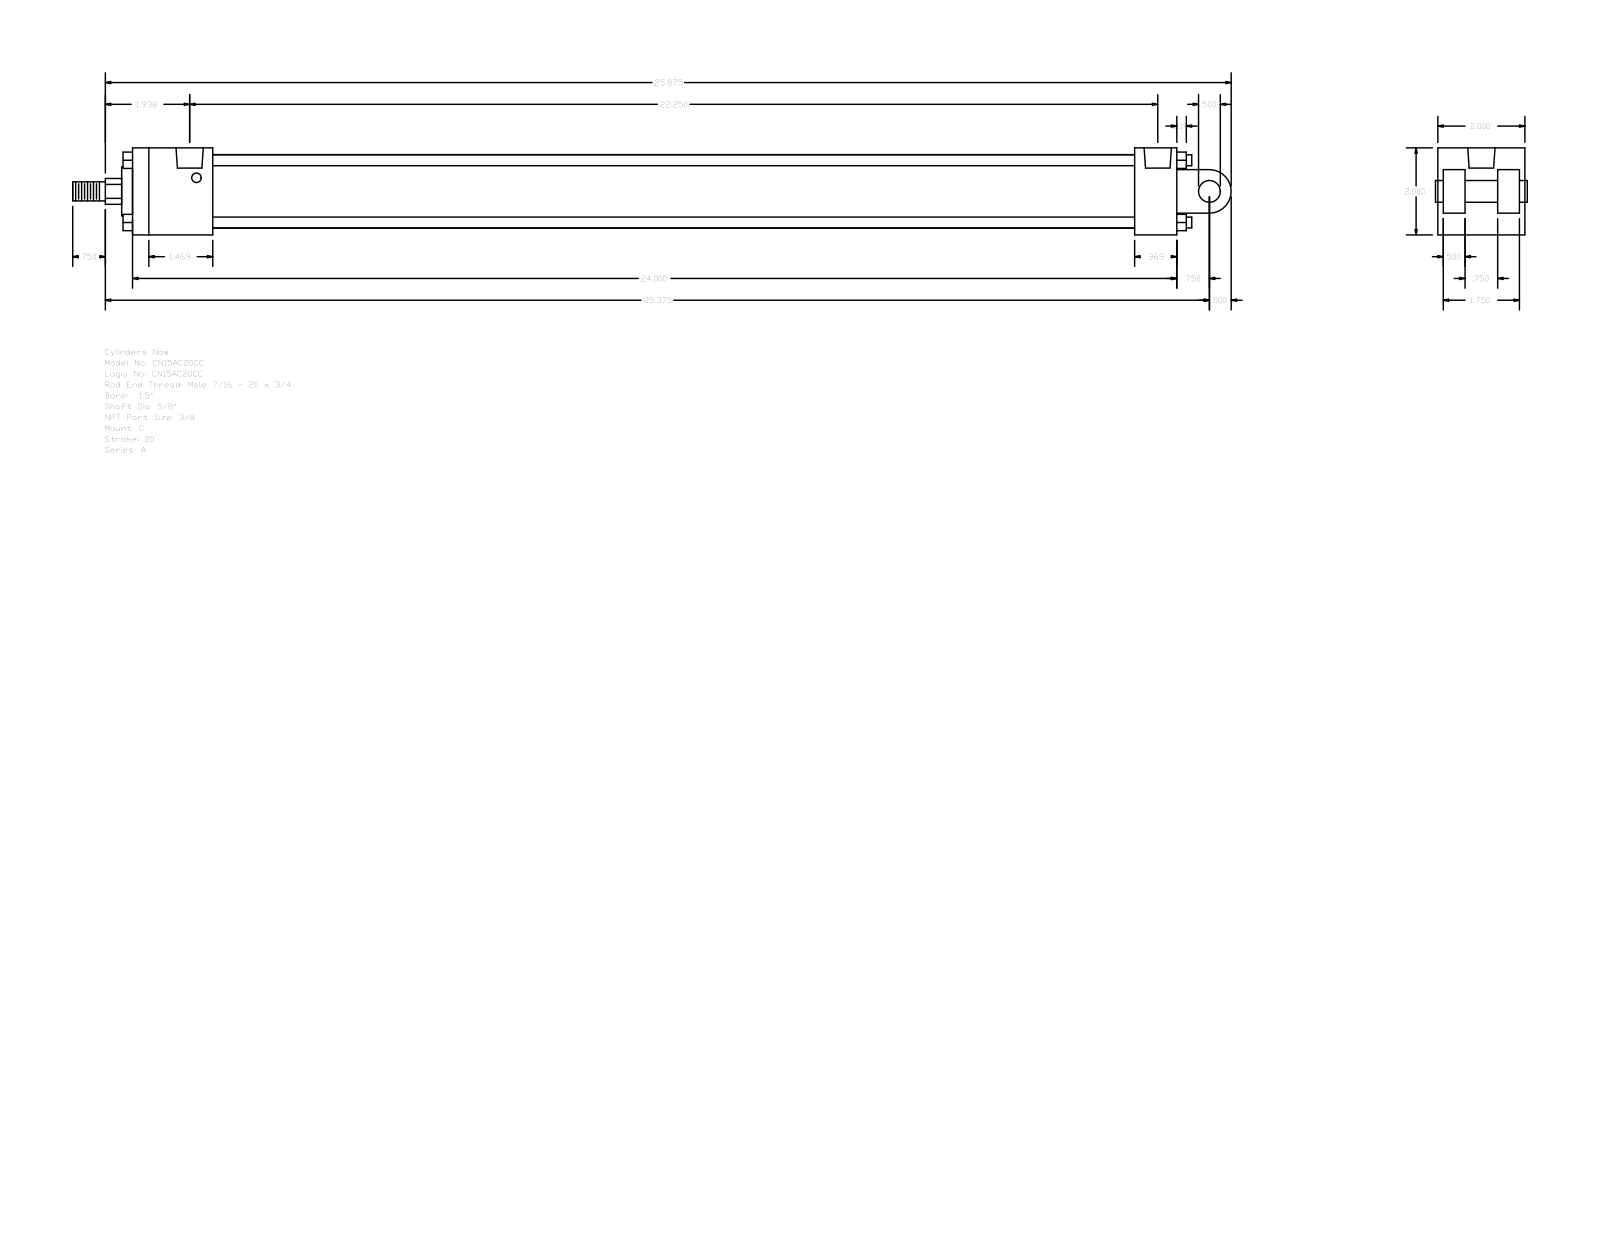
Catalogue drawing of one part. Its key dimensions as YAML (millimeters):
part_name: "A_C__0150_0.625"
step_written_by: "GSSL Pune (CONFIG_CONTROL_DESIGN)"
units: millimeters
bodies: {solids: 0, faces: 135, planar: 102, cylindrical: 33, other: 0}
overall_size: [676.27, 50.8, 50.8]
round_holes:
  - {diameter: 5.56, count: 4}
  - {diameter: 15.93, count: 2}
round_bosses_or_shafts:
  - {diameter: 6.35, count: 4}
  - {diameter: 42.93, count: 1}
  - {diameter: 28.57, count: 1}
  - {diameter: 15.88, count: 1}
  - {diameter: 12.7, count: 1}
  - {diameter: 11.11, count: 1}
partial_cylinders:
  - {radius: 7.54, count: 1}
  - {radius: 12.7, count: 1}
face_to_face_distances: [50.8, 12.7, 609.6, 34.93, 3.17, 47.63, 15.87, 31.76, 584.99, 24.61]
hole_center_spacings: [3.97, 557.21, 561.18, 565.15]
